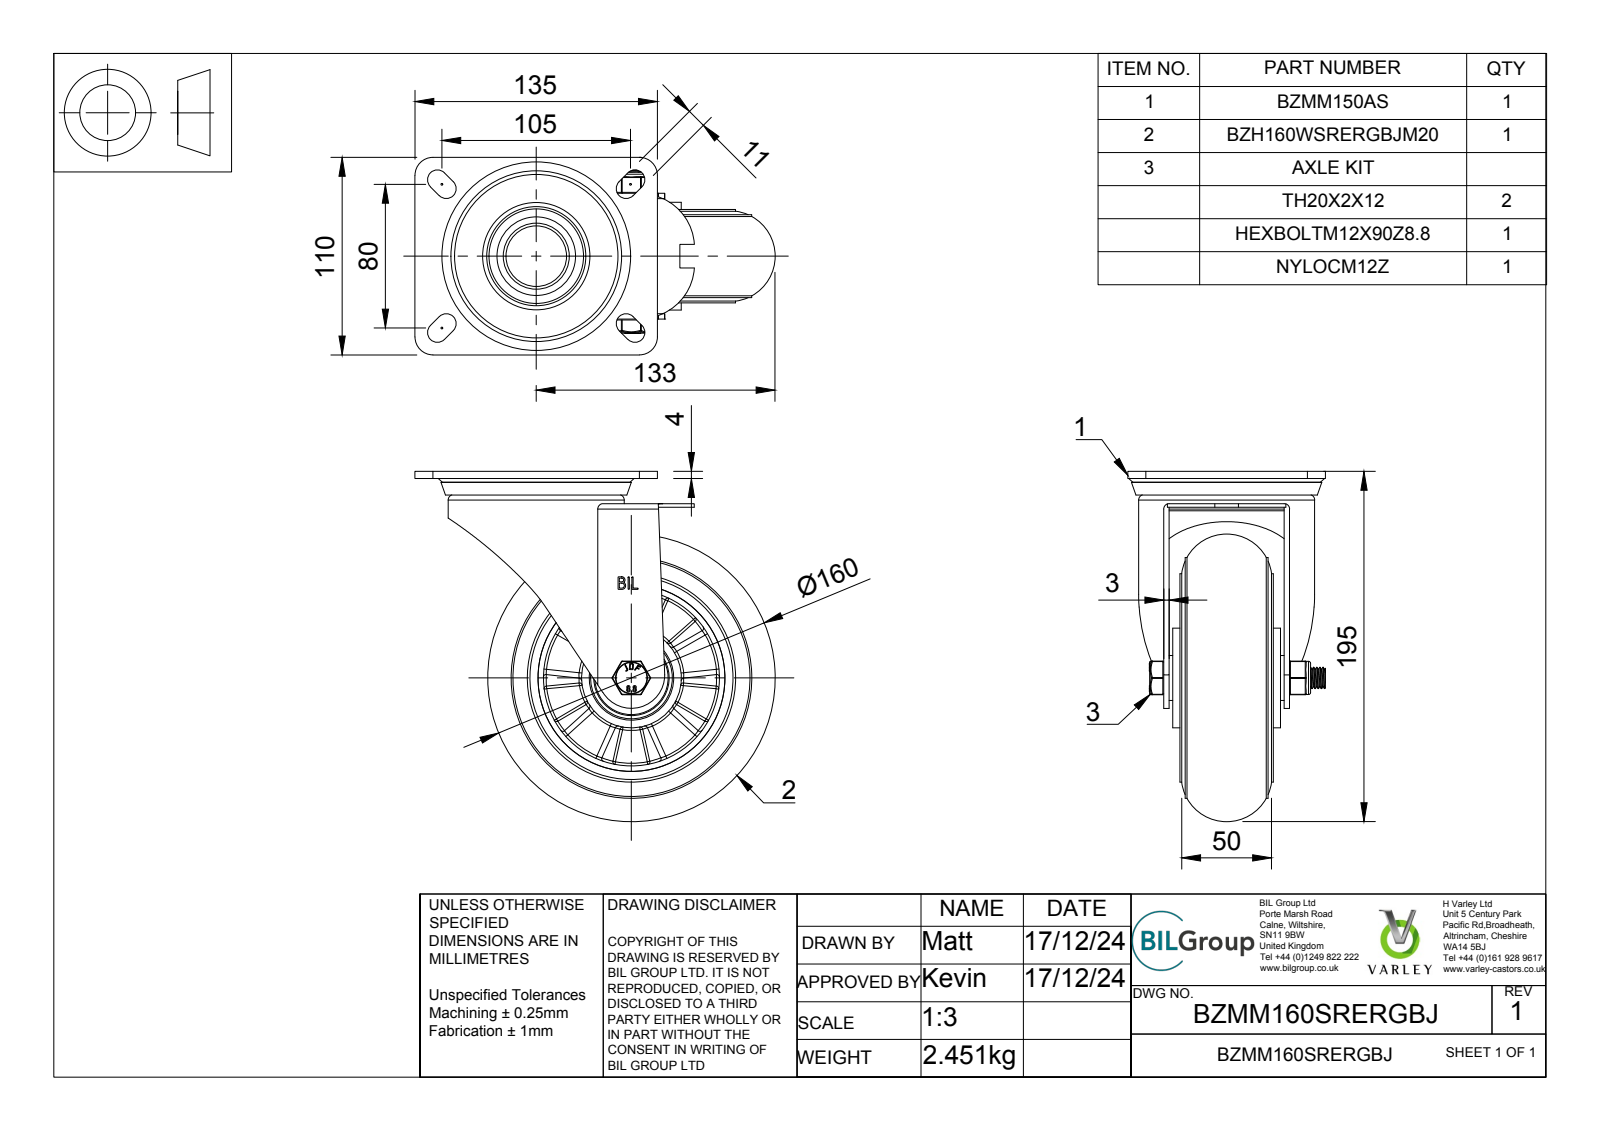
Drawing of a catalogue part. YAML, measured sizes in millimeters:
part_name: "BZMM160SRERGBJ v3; BZMM150AS - 2 - 64 v2; ZINC PLATED, PRESSED STEEL TOP PLATE; ZINC PLATED, PRESSED STEEL TOP PLATE Geometry (+7 more)"
step_written_by: "Autodesk Translation Framework v13.20.0.188 (AP242_MANAGED_MODEL_BASED_3D_ENGINEERING_MIM_LF)"
units: millimeters
bodies: {solids: 77, faces: 1368, planar: 455, cylindrical: 216, other: 697}
overall_size: [200.5, 195, 110]
volume: 810826
surface_area: 283779
round_holes:
  - {diameter: 12, count: 1}
  - {diameter: 12.2, count: 1}
  - {diameter: 14, count: 1}
  - {diameter: 20, count: 1}
  - {diameter: 28.5, count: 1}
  - {diameter: 30.8, count: 1}
  - {diameter: 33.75, count: 1}
  - {diameter: 39.75, count: 1}
  - {diameter: 40.3, count: 1}
  - {diameter: 40.5, count: 1}
  - {diameter: 42, count: 1}
  - {diameter: 47, count: 1}
round_bosses_or_shafts:
  - {diameter: 134, count: 1}
  - {diameter: 116, count: 1}
  - {diameter: 98, count: 1}
  - {diameter: 78, count: 1}
  - {diameter: 55.5, count: 1}
  - {diameter: 50, count: 1}
  - {diameter: 40.8, count: 1}
  - {diameter: 31.3, count: 1}
partial_cylinders:
  - {radius: 0.5, count: 20}
  - {radius: 5.5, count: 8}
  - {radius: 0.47, count: 4}
  - {radius: 0.9, count: 4}
  - {radius: 10, count: 4}
  - {radius: 0.89, count: 2}
  - {radius: 0.89, count: 2}
  - {radius: 1.5, count: 2}
face_to_face_distances: [9, 7, 3, 5, 4, 2, 14, 16, 10, 50]
